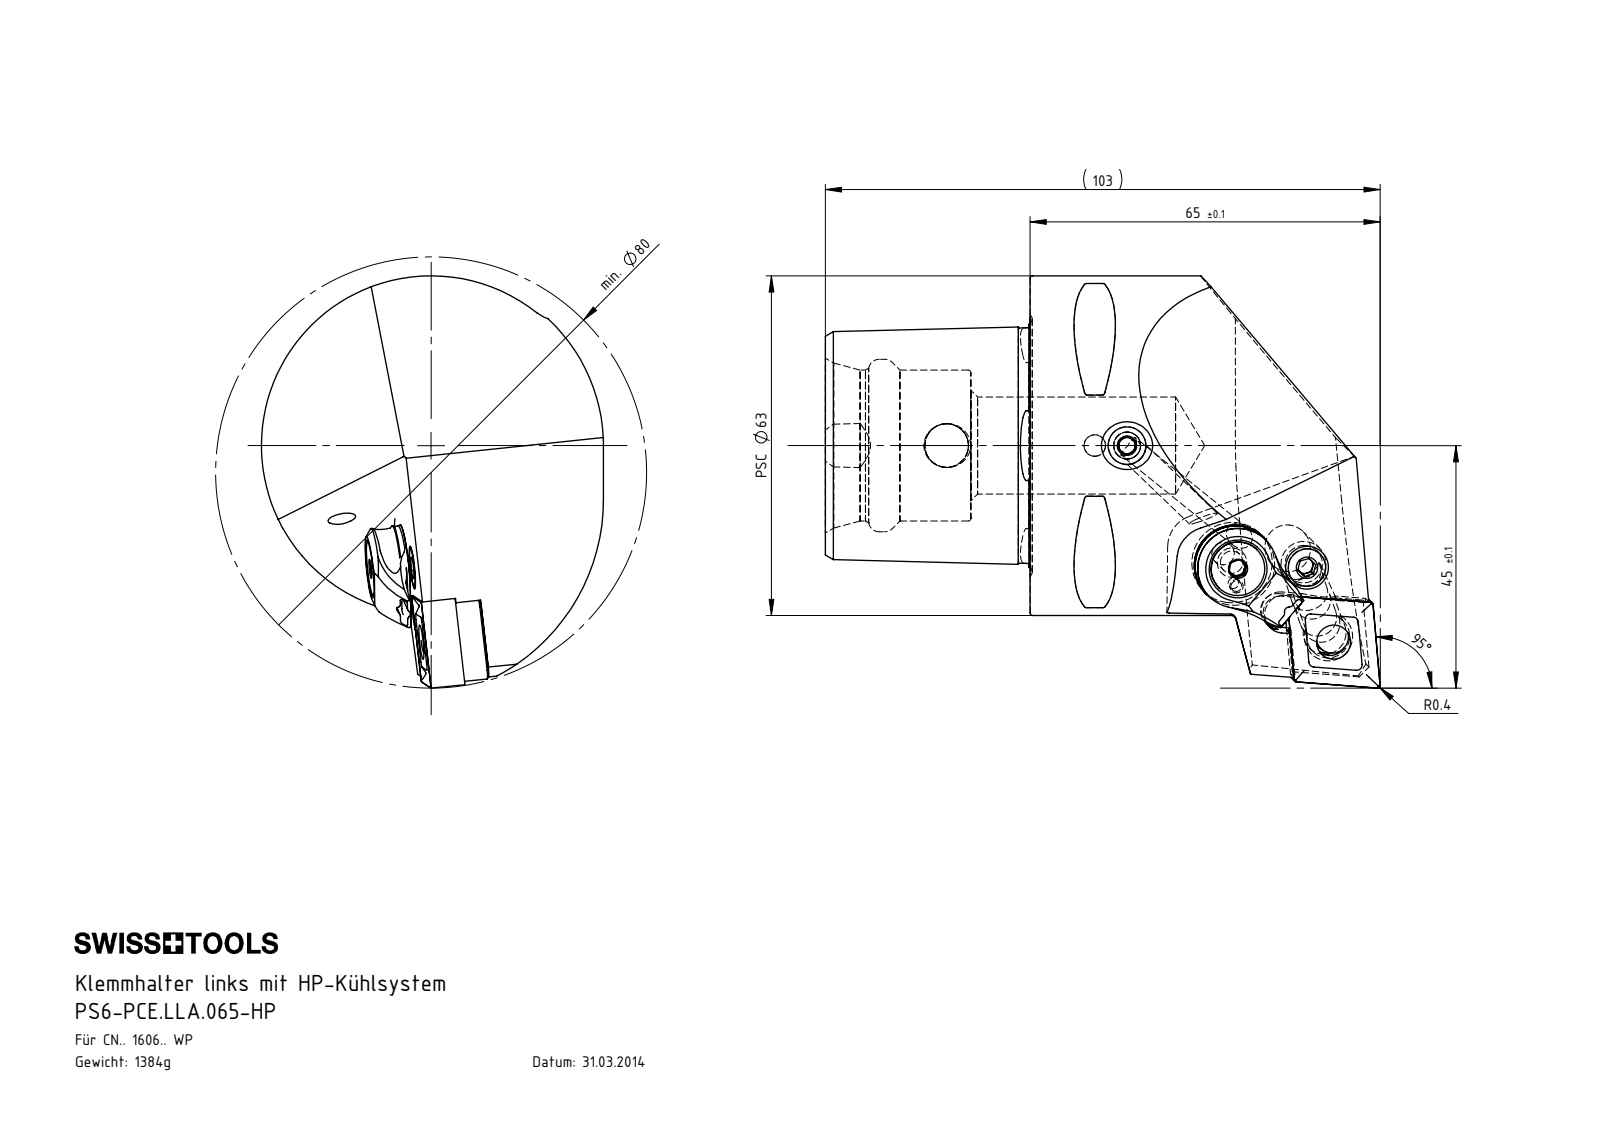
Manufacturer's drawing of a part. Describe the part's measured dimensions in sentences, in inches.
The part is named "WCE-ER4.101.020_A; CHP-ER1.008.014_A; WCE-ER3.101.000_A; PS6-PCE.LLA.065-HP_B (+8 more)". Its 3-D file was written by "SolidWorks 2017 (CONFIG_CONTROL_DESIGN)". It is 12 solids with 434 faces: 147 planar, 105 cylindrical and 182 other. Overall it measures 4.055 by 3.012 by 2.52 inches. Its volume is 11.27 cubic inches and its surface area 56.58 square inches. Round holes: 3 of diameter 0.165, 2 of diameter 0.276, 1 of diameter 0.047, 1 of diameter 0.079, 1 of diameter 0.118, 1 of diameter 0.157, 1 of diameter 0.197, 1 of diameter 0.209, 1 of diameter 0.25, 1 of diameter 0.317, 1 of diameter 0.319, 1 of diameter 0.331. Round bosses or shafts: 2 of diameter 0.315, 1 of diameter 2.48, 1 of diameter 0.585, 1 of diameter 0.528, 1 of diameter 0.394, 1 of diameter 0.311, 1 of diameter 0.252, 1 of diameter 0.236. Partial cylindrical surfaces (rounded edges, fillets, slot ends): 12 of radius 0.02, 7 of radius 0.039, 5 of radius 0.138, 4 of radius 0.016, 4 of radius 0.059, 4 of radius 0.236, 3 of radius 0.012, 2 of radius 0.043. The main face-to-face distances are 1.496, 0.238, 0.98, 0.433, 0.187, 0.426, 1.063, 0.031, 0.595, 2.197. The hole center spacings are 0.177, 0.443, 0.801, 0.811, 0.475, 0.581, 0.591, 0.709.
